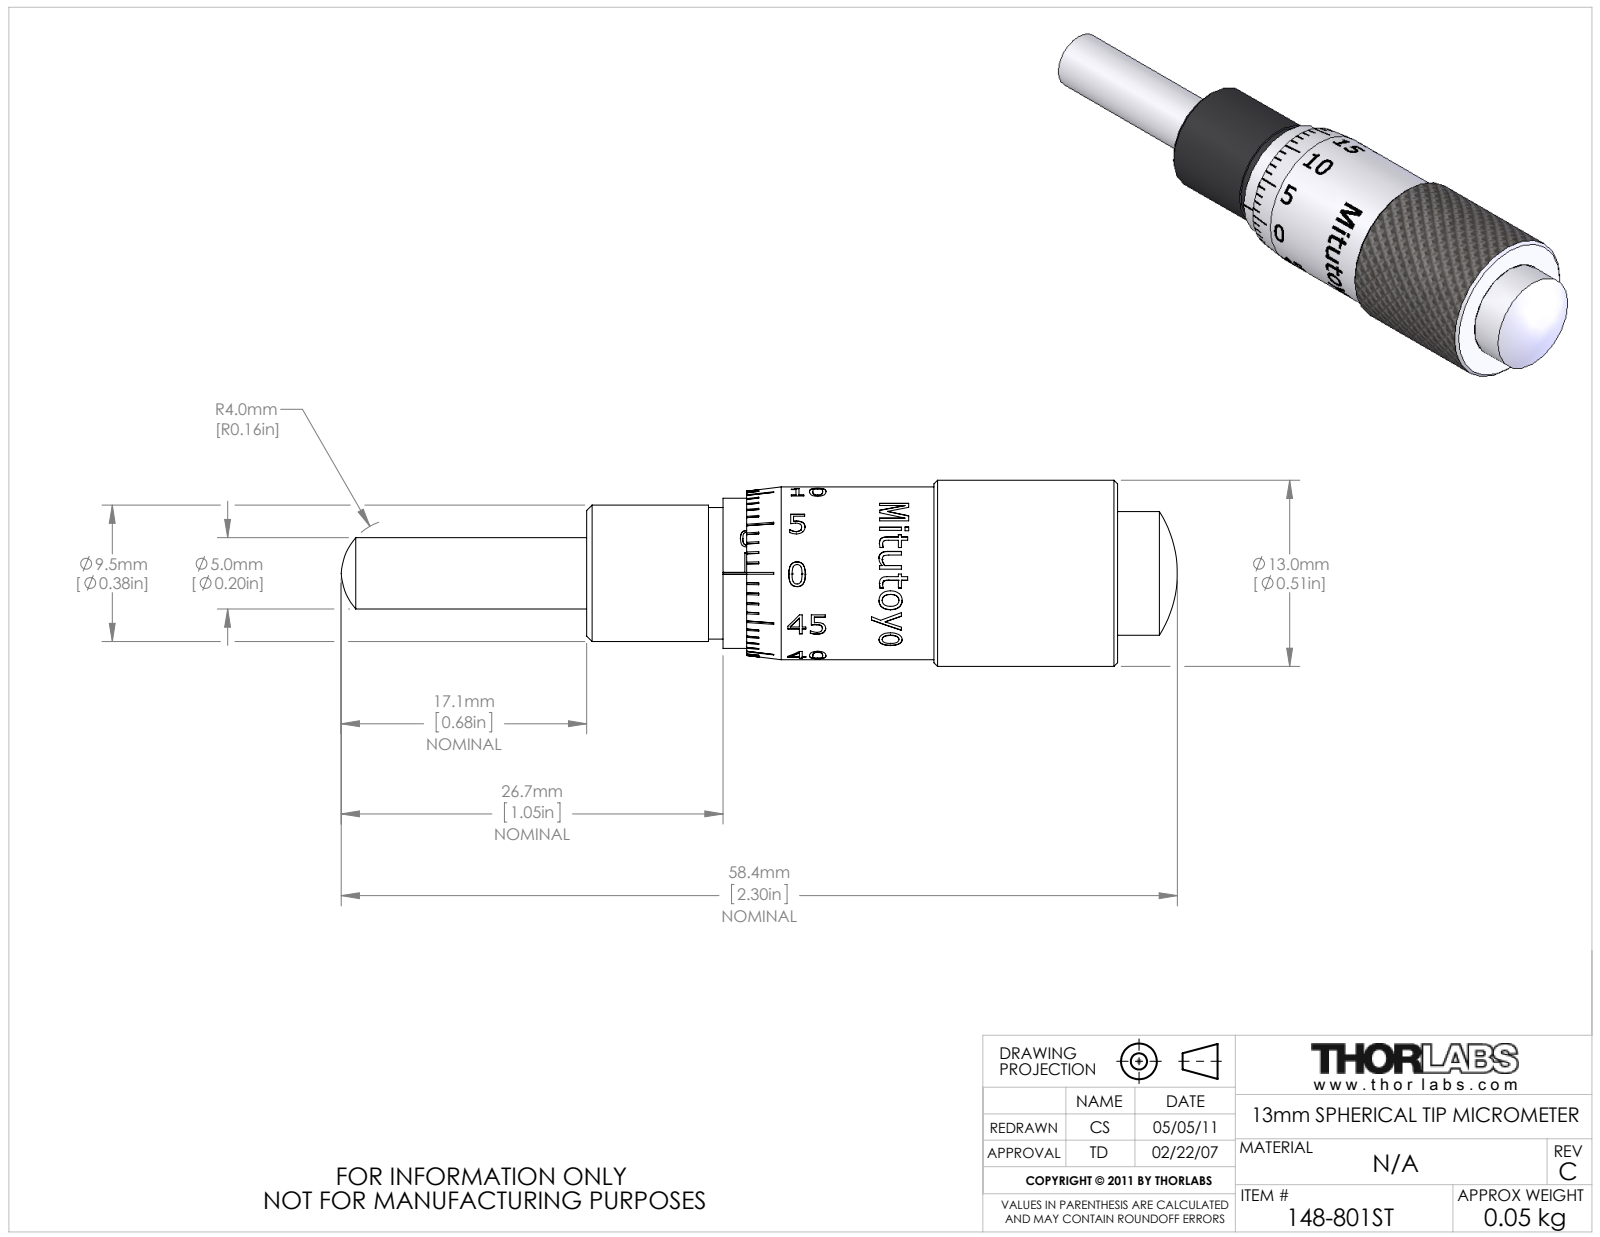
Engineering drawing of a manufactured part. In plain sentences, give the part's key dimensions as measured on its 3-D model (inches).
The part is named "13431-E0W". Its 3-D file was written by "SolidWorks 2012 (AUTOMOTIVE_DESIGN)". It is 2 solids with 827 faces: 392 planar, 114 cylindrical and 321 other. Overall it measures 2.299 by 0.512 by 0.512 inches. Its volume is 0.263 cubic inches and its surface area 6.863 square inches. Round holes: 1 of diameter 0.197, 1 of diameter 0.42. Round bosses or shafts: 1 of diameter 0.512, 1 of diameter 0.475, 1 of diameter 0.413, 1 of diameter 0.386, 1 of diameter 0.375, 1 of diameter 0.362, 1 of diameter 0.34, 1 of diameter 0.196. Partial cylindrical surfaces (rounded edges, fillets, slot ends): 1 of radius 0.205, 1 of radius 0.23, 1 of radius 0.235, 1 of radius 0.236. The main face-to-face distances are 0.188, 0.235, 0.047, 1.46, 1.272, 1.225, 1.085, 0.897, 0.85, 0.375.
